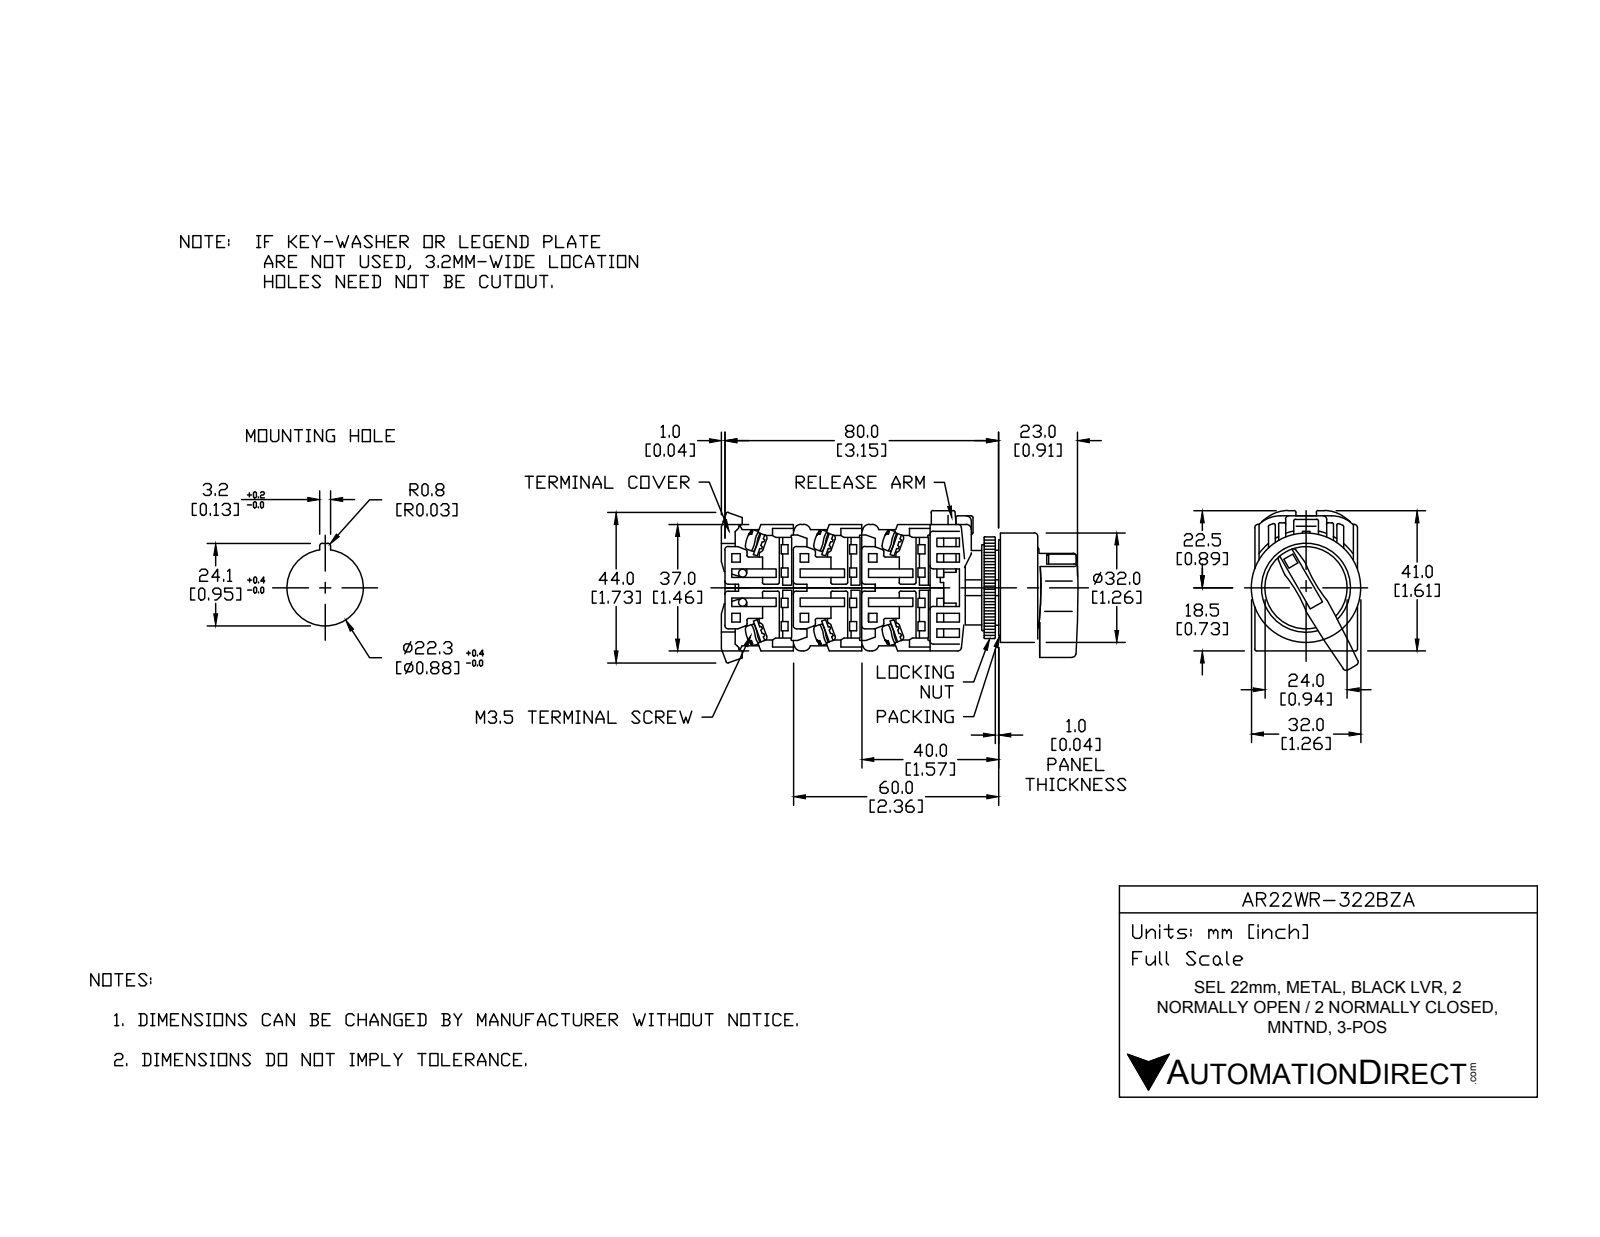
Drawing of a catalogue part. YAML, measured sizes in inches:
part_name: "AR22WR-322BZA"
step_written_by: "SolidWorks 2017 (AUTOMOTIVE_DESIGN)"
units: inches
bodies: {solids: 18, faces: 467, planar: 318, cylindrical: 121, other: 28}
overall_size: [2.52, 1.969, 1.26]
volume: 2.398
surface_area: 39.1
round_holes:
  - {diameter: 0.858, count: 1}
  - {diameter: 0.866, count: 1}
  - {diameter: 0.984, count: 1}
  - {diameter: 1.22, count: 1}
round_bosses_or_shafts:
  - {diameter: 0.197, count: 4}
  - {diameter: 1.26, count: 1}
  - {diameter: 1.201, count: 1}
  - {diameter: 1.173, count: 1}
  - {diameter: 0.945, count: 1}
  - {diameter: 0.856, count: 1}
  - {diameter: 0.669, count: 1}
partial_cylinders:
  - {radius: 0.02, count: 39}
  - {radius: 0.039, count: 10}
  - {radius: 0.069, count: 8}
  - {radius: 0.197, count: 4}
  - {radius: 0.157, count: 2}
  - {radius: 0.653, count: 1}
  - {radius: 0.693, count: 1}
face_to_face_distances: [0.039, 0.709, 0.118, 1.122, 0.787, 1.909, 1.142, 0.02, 0.394, 0.827]
